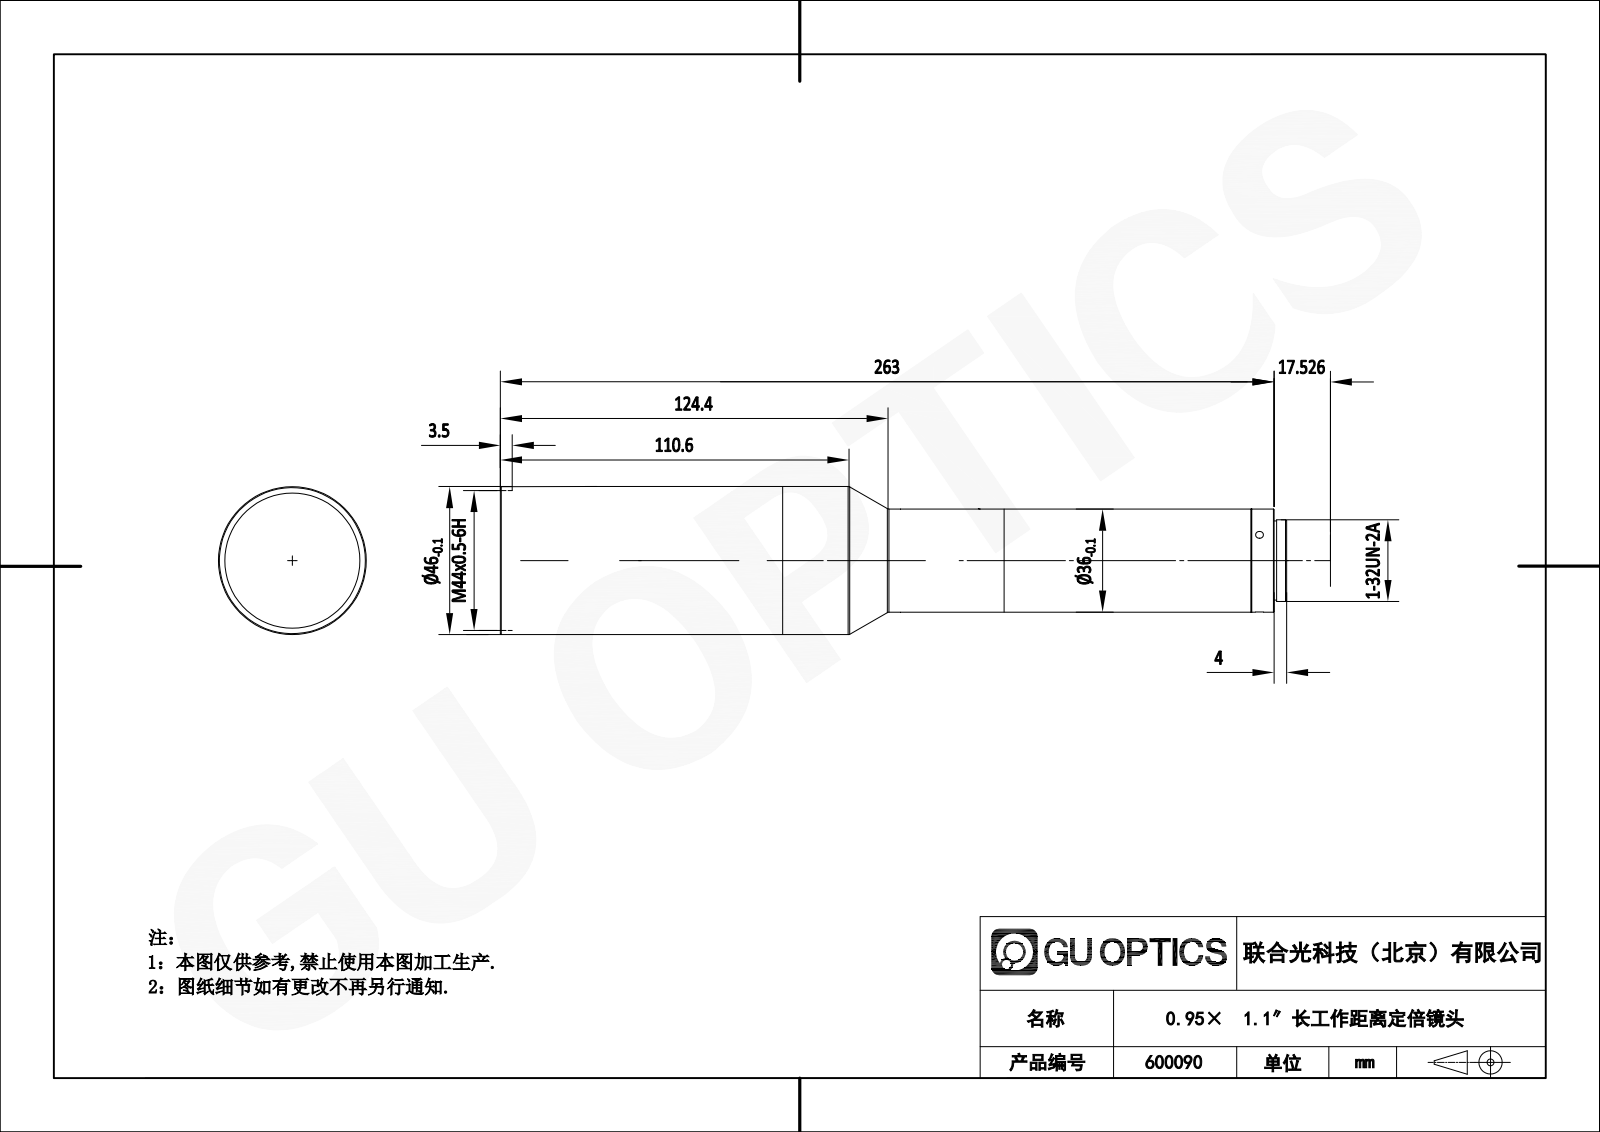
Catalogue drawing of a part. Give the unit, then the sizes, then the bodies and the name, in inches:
Units: inches
Overall size (bounding box): 10.514 × 1.811 × 1.811
Round holes (diameter × count): ⌀0.098 ×3, ⌀1.654 ×1
Round bosses / shafts (diameter × count): ⌀1.811 ×1, ⌀1.417 ×1, ⌀1 ×1, ⌀0.969 ×1
Partial cylindrical surfaces — rounded edges, fillets, slot ends (radius × count): R0.694 ×1
Main face-to-face distances: 10.002, 0.157, 10.159, 10.513, 10.356, 0.354, 0.126, 0.031, 10.033, 10.387
Volume: 20.7 in³ · Surface area: 63.39 in²
Bodies: 2 solids, 28 faces (7 planar, 12 cylindrical, 9 other)
Part name (STEP PRODUCT): 600090
STEP written by: SolidWorks 2020 (AUTOMOTIVE_DESIGN)
